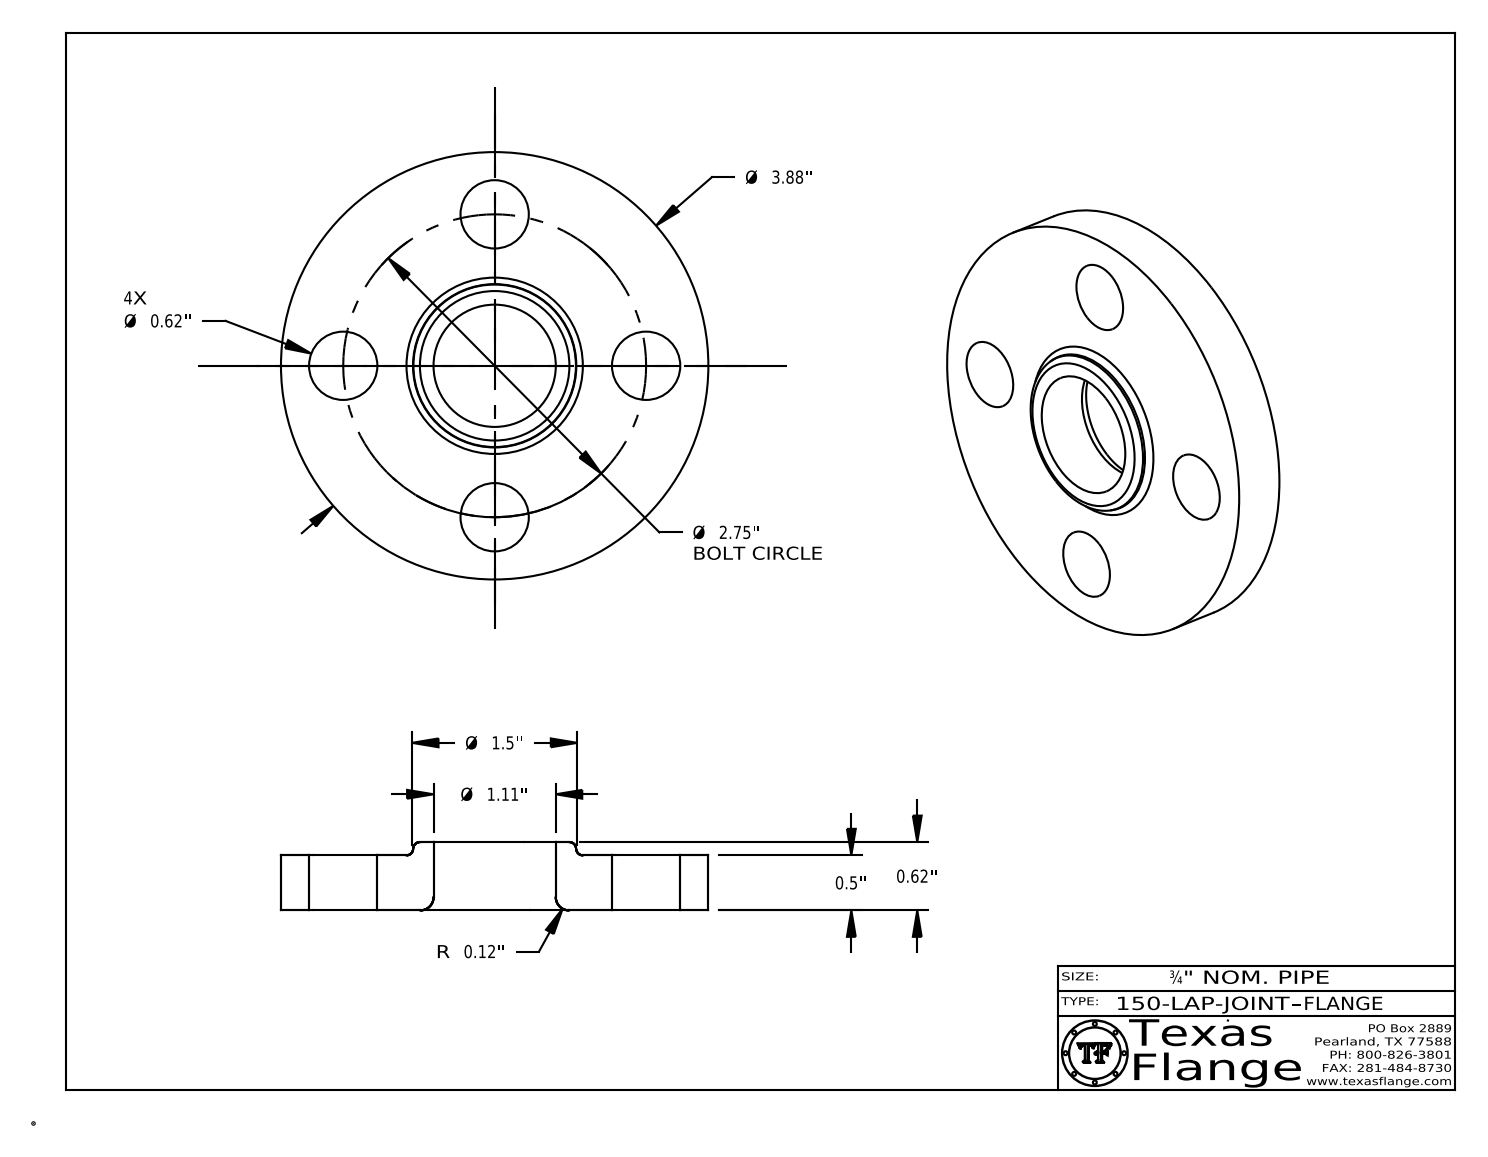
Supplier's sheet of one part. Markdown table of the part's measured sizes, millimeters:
| quantity | value |
| --- | --- |
| part name | 150-LAP-JOINT FLANGE |
| STEP written by | CATIA V5 STEP AP214 (AUTOMOTIVE_DESIGN) |
| units | millimeters |
| bodies | 1 solid, 408 faces (368 planar, 32 cylindrical, 8 other) |
| overall size | 98.6 × 98.6 × 15.7 |
| volume | 80 330 mm³ |
| surface area | 20 440 mm² |
| round holes (diameter × count) | 15.7 × 4, 12.6 × 1, 28.2 × 1 |
| round bosses / shafts (diameter × count) | 0.8 × 8, 98.6 × 1, 9.9 × 1 |
| main face-to-face distances | 12.7, 15.7, 3, 12.3, 0.4, 3.4, 3.8, 3.7, 0.7, 3.1 |
| hole center spacings | 34.9, 49.4, 26.7, 64.5, 69.9 |
